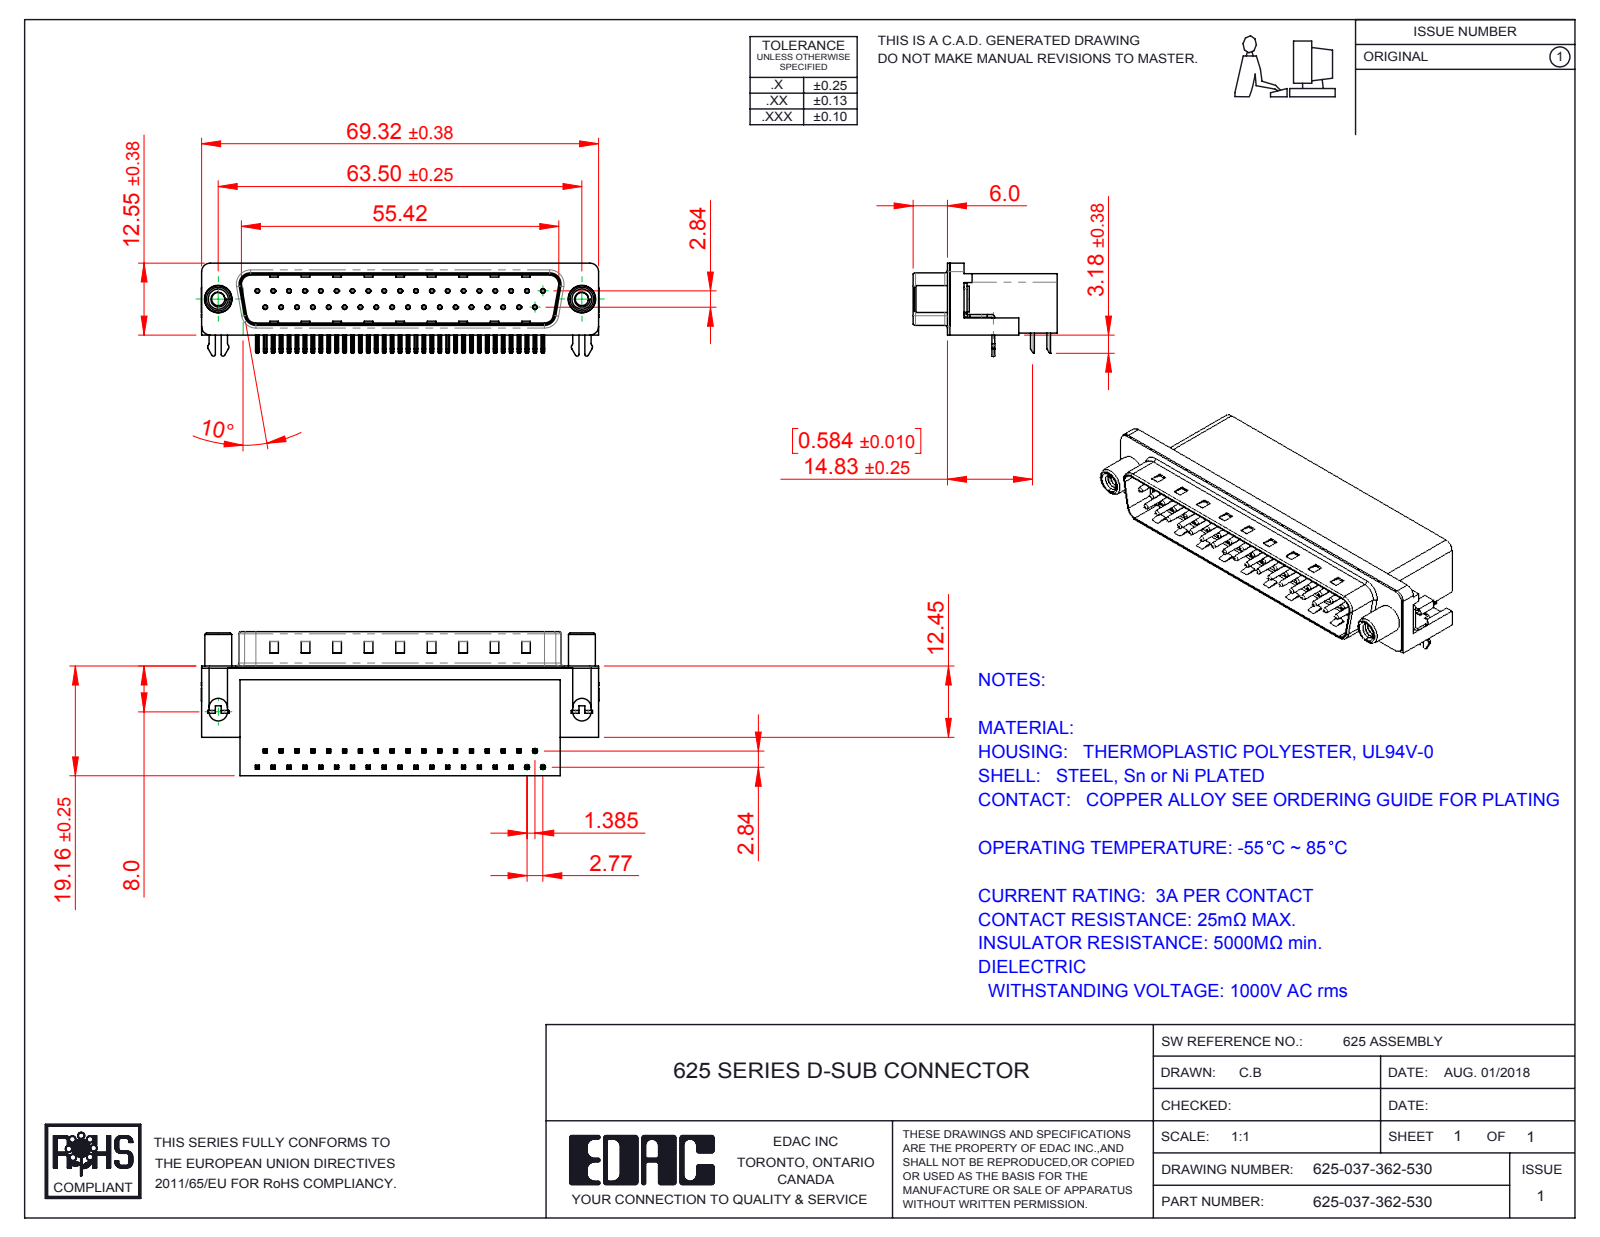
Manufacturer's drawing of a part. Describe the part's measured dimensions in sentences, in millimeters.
The part is named "625 Contact Top; 625-037-362-530; 625 Contact Bottom; 625 Housing_37 Socket (+3 more)". Its 3-D file was written by "SolidWorks 2016 (CONFIG_CONTROL_DESIGN)". It is 43 solids with 3235 faces: 2037 planar, 933 cylindrical and 265 other. Overall it measures 69.4 by 25.16 by 16.25 millimeters. Its volume is 12 690 cubic millimeters and its surface area 11 959 square millimeters. Round holes: 37 of diameter 0.35, 37 of diameter 0.8, 2 of diameter 2.3, 2 of diameter 3.1, 2 of diameter 4, 2 of diameter 4.8, 2 of diameter 5. Round bosses or shafts: 37 of diameter 0.75, 2 of diameter 4.9, 2 of diameter 4.7, 2 of diameter 4.5, 2 of diameter 3.85. Partial cylindrical surfaces (rounded edges, fillets, slot ends): 148 of radius 0.25, 74 of radius 0.12, 16 of radius 1, 14 of radius 0.5, 8 of radius 1.6, 7 of radius 1.5, 4 of radius 0.32, 4 of radius 0.9. The main face-to-face distances are 10.34, 0.4, 18.76, 8.76, 2.84, 19.16, 2.09, 10.1, 1.74, 8.36. The hole center spacings are 3.16, 2.77, 5.54, 8.31, 11.08, 13.85, 19.39, 22.16.
